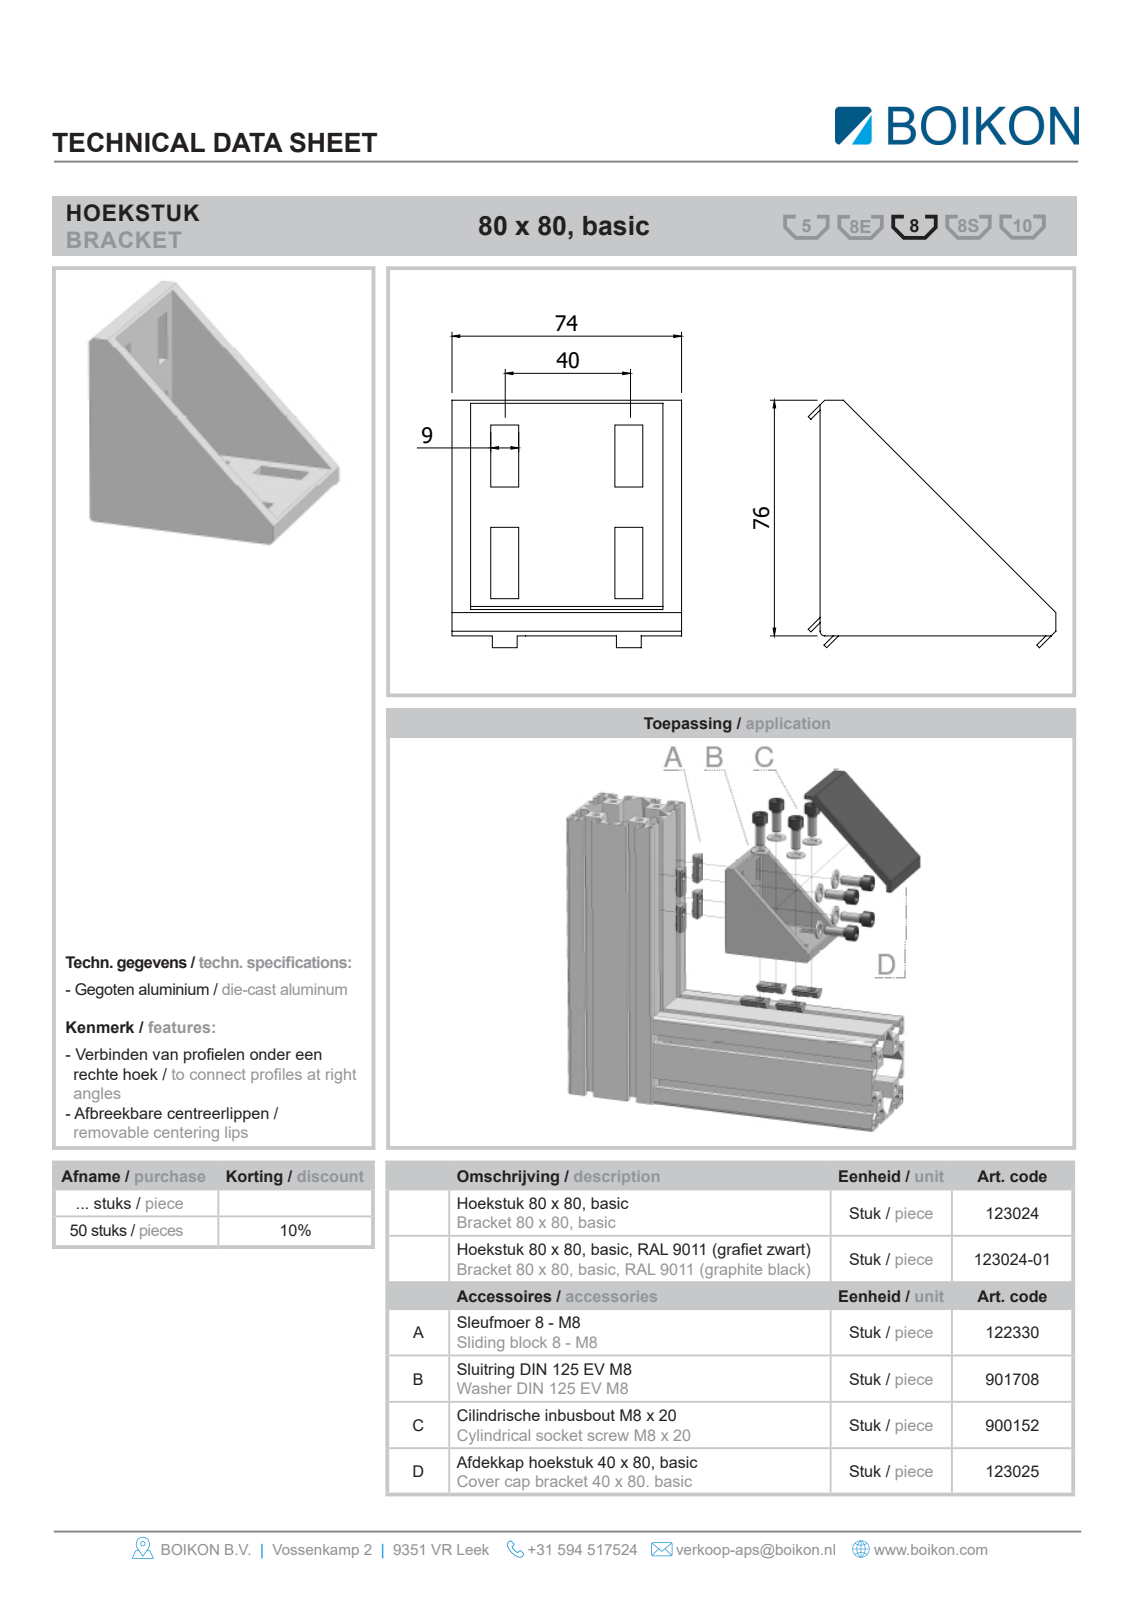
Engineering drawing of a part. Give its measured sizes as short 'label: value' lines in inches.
name: Root; 123024HOEKSTUK 80X80 BASICBOIKON; 122330Sleufmoer 8 - M8 met kogelBOIKON; 900152Cil. inbusbout DIN 912 EV M8 x 20BOIKON0 (+2 more)
written by: HiCAD 2013 1802.4 Build 509 (AUTOMOTIVE_DESIGN)
unit: in
bodies: 26 solids, 557 faces (387 planar, 130 cylindrical, 40 other)
size: 3.628 × 3.628 × 2.913
volume: 9.914 in³; area: 114.9 in²
holes: 8× ⌀0.315, 8× ⌀0.331
bosses: 8× ⌀0.63, 8× ⌀0.512, 8× ⌀0.255
rounds: 15× R0.039, 8× R0.02, 8× R0.079, 4× R0.197, 1× R0.059
face distances: 0.236, 0.335, 2.677, 2.913, 0.157, 0.177, 2.441, 0.24, 0.398, 2.185
hole spacings: 1.28, 1.575, 2.029
